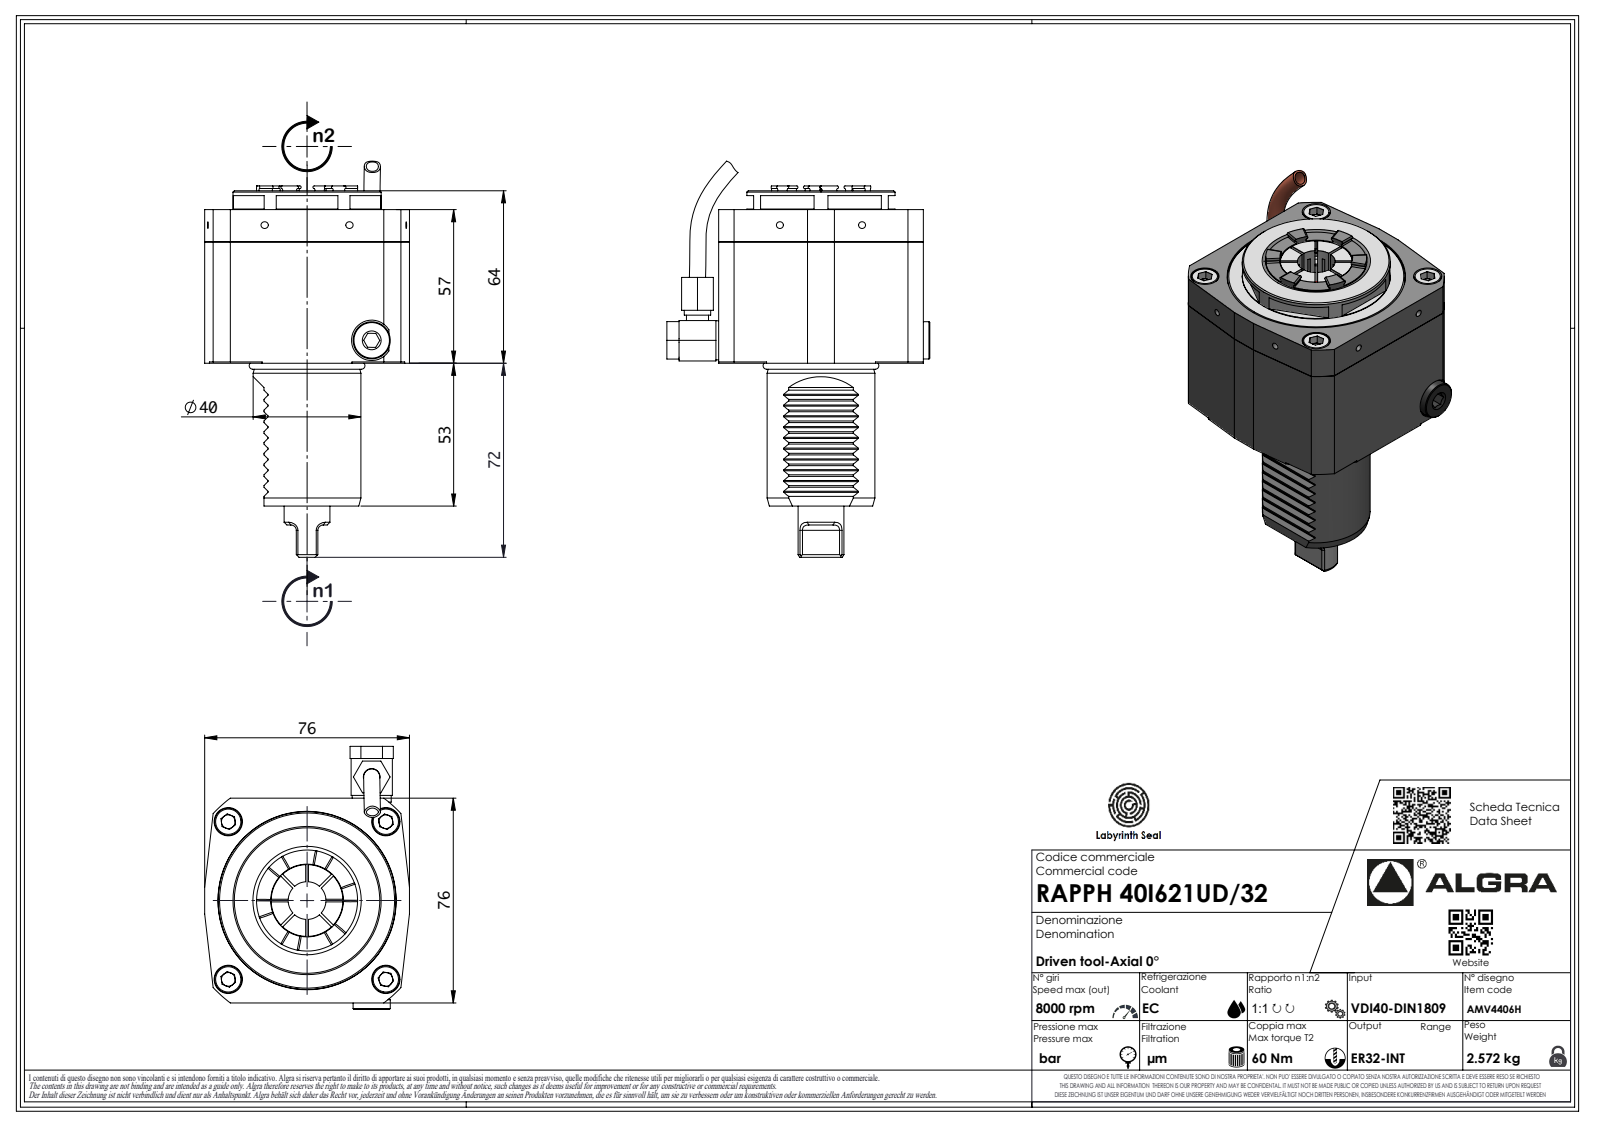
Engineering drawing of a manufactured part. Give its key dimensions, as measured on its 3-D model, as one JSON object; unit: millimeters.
{"part_name": "RAPPH40I621UD32", "step_written_by": "SolidWorks 2023 (AUTOMOTIVE_DESIGN)", "units": "millimeters", "bodies": {"solids": 1, "faces": 637, "planar": 414, "cylindrical": 90, "other": 133}, "overall_size": [146.99, 97.95, 76], "volume_mm3": 397432, "surface_area_mm2": 41984, "round_holes": [[2.1, 1], [14, 1], [15, 1], [27, 1], [33.45, 1], [38.5, 1]], "round_bosses_or_shafts": [[55, 1], [40, 1], [38.7, 1], [37.5, 1], [29.2, 1], [17, 1], [14.5, 1], [13.8, 1]], "partial_cylinders_radius": [[0.3, 10], [0.33, 7], [0.52, 7], [3.7, 7], [2, 2], [0.21, 1], [7.65, 1], [41.5, 1]], "face_to_face_distances": [76, 57, 76.62, 64, 7, 53, 110, 117, 2.83, 1], "hole_center_spacings": [41.65]}
